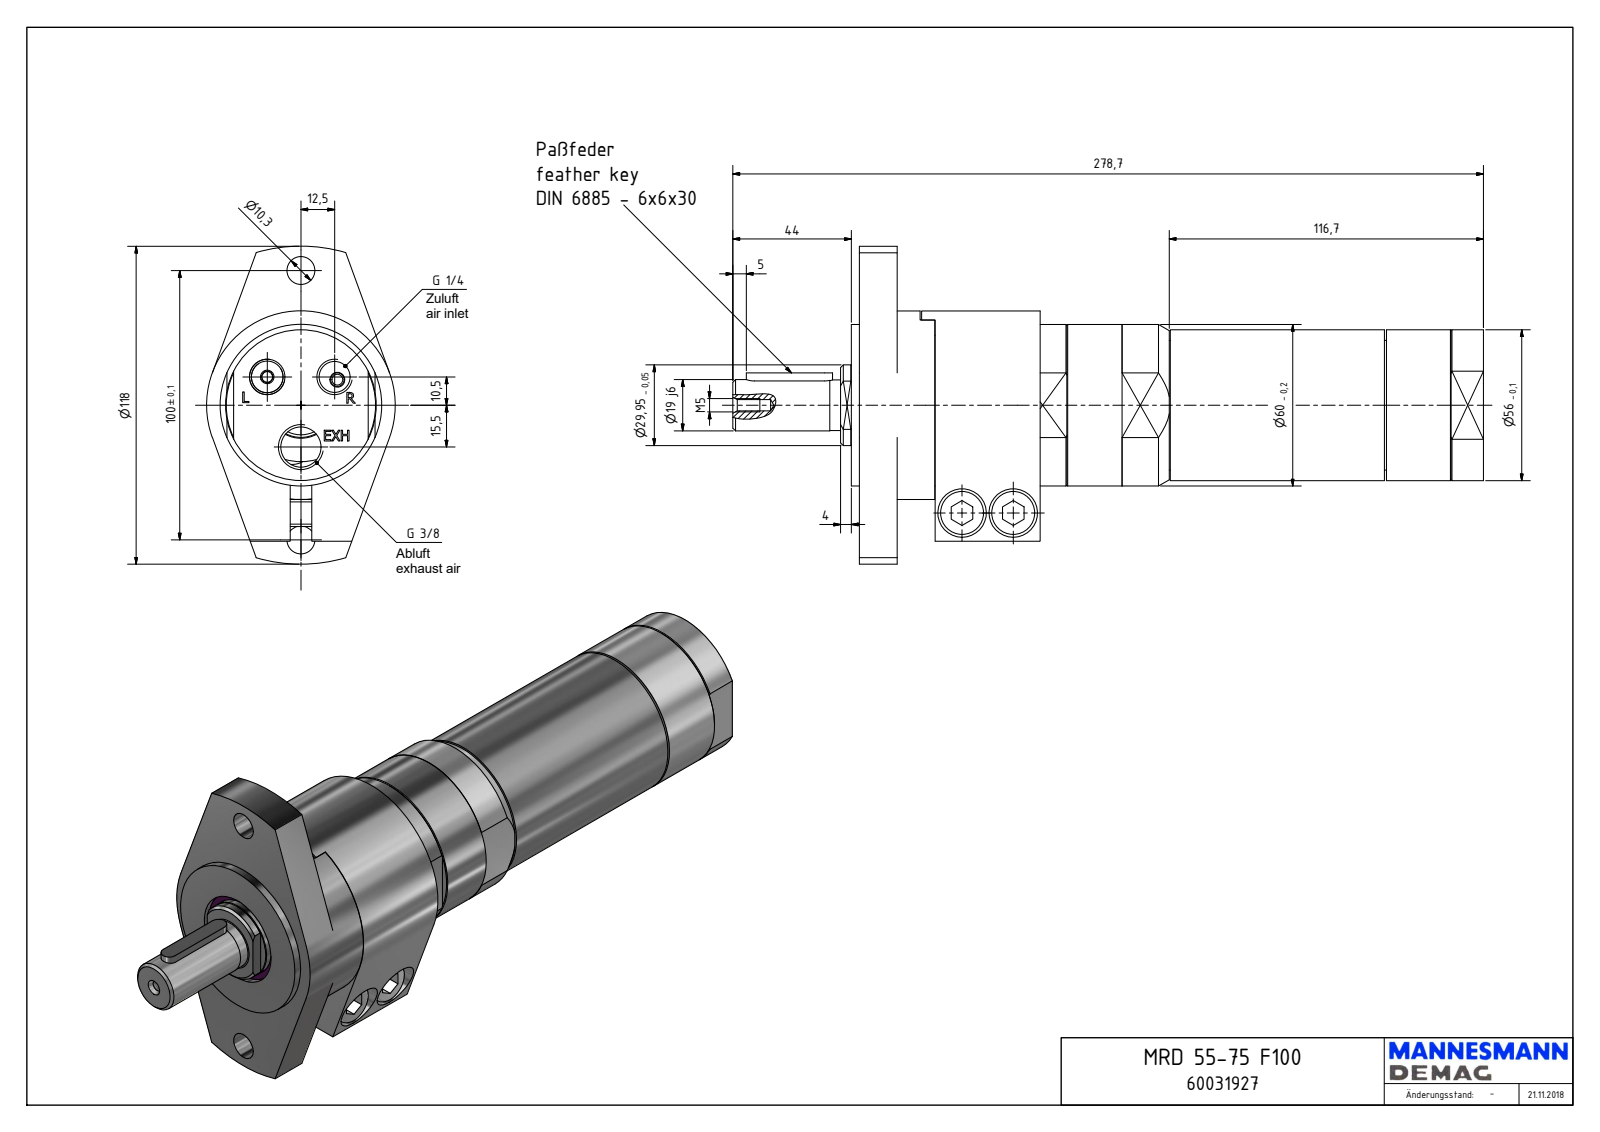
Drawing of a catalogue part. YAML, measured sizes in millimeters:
part_name: "MRD 55-75 F100_60031927"
step_written_by: "Autodesk Inventor 2018 (AUTOMOTIVE_DESIGN)"
units: millimeters
bodies: {solids: 1, faces: 285, planar: 167, cylindrical: 64, other: 54}
overall_size: [278.7, 118, 70]
volume: 748495
surface_area: 82298
round_holes:
  - {diameter: 4, count: 2}
  - {diameter: 8.38, count: 2}
  - {diameter: 10.3, count: 2}
  - {diameter: 10.5, count: 2}
  - {diameter: 11.45, count: 2}
  - {diameter: 18, count: 2}
  - {diameter: 1.55, count: 1}
  - {diameter: 4.13, count: 1}
  - {diameter: 5.5, count: 1}
  - {diameter: 14.95, count: 1}
  - {diameter: 35, count: 1}
  - {diameter: 36.5, count: 1}
round_bosses_or_shafts:
  - {diameter: 16, count: 2}
  - {diameter: 10, count: 2}
  - {diameter: 70, count: 1}
  - {diameter: 60, count: 1}
  - {diameter: 56, count: 1}
  - {diameter: 55.18, count: 1}
  - {diameter: 48.18, count: 1}
  - {diameter: 29.95, count: 1}
partial_cylinders:
  - {radius: 3, count: 2}
  - {radius: 6, count: 2}
  - {radius: 19.14, count: 1}
  - {radius: 23, count: 1}
  - {radius: 25.81, count: 1}
  - {radius: 59, count: 1}
face_to_face_distances: [14, 17, 3, 231.7, 217.7, 234.7, 70.1, 67.1, 53.1, 164.6]
hole_center_spacings: [16.32, 28.85, 41.43, 50, 61.78, 15.5, 19, 25]
